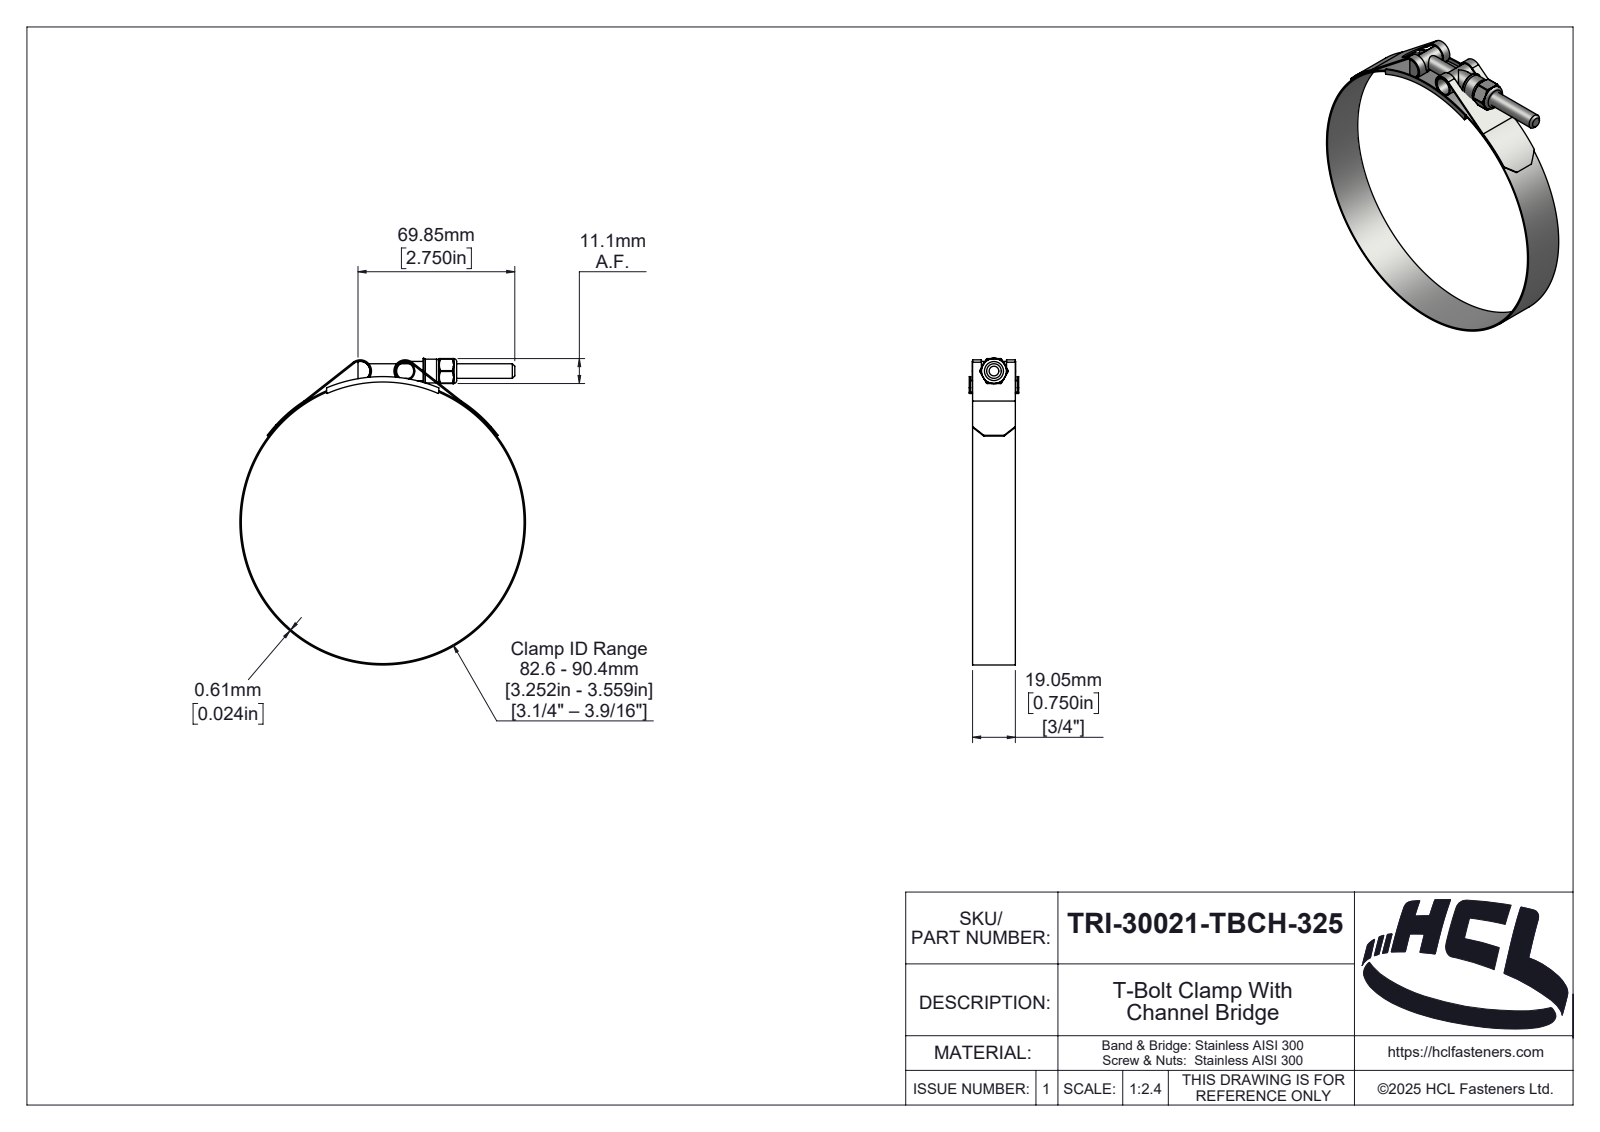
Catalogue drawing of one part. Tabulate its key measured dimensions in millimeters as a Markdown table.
| quantity | value |
| --- | --- |
| part name | TRI-30021-TBCH-325 |
| STEP written by | SolidWorks 2025 (AUTOMOTIVE_DESIGN) |
| units | millimeters |
| bodies | 6 solids, 330 faces (46 planar, 122 cylindrical, 162 other) |
| overall size | 136.59 × 127.22 × 22 |
| volume | 10 567 mm³ |
| surface area | 26 082 mm² |
| round holes (diameter × count) | 5.4 × 1, 6.35 × 1, 6.5 × 1, 7.58 × 1, 126 × 1 |
| round bosses / shafts (diameter × count) | 8.58 × 2, 127.22 × 1, 10.58 × 1 |
| partial cylindrical surfaces (radius × count) | 0.39 × 6, 0.5 × 2, 4.39 × 2, 5 × 2, 0.59 × 1, 2.42 × 1, 3.03 × 1, 3.19 × 1 |
| main face-to-face distances | 0.61, 19.06, 1.47, 20.53, 21.39, 0.86, 19.92, 0.74, 22, 11.12 |
| hole center spacings | 68 |
